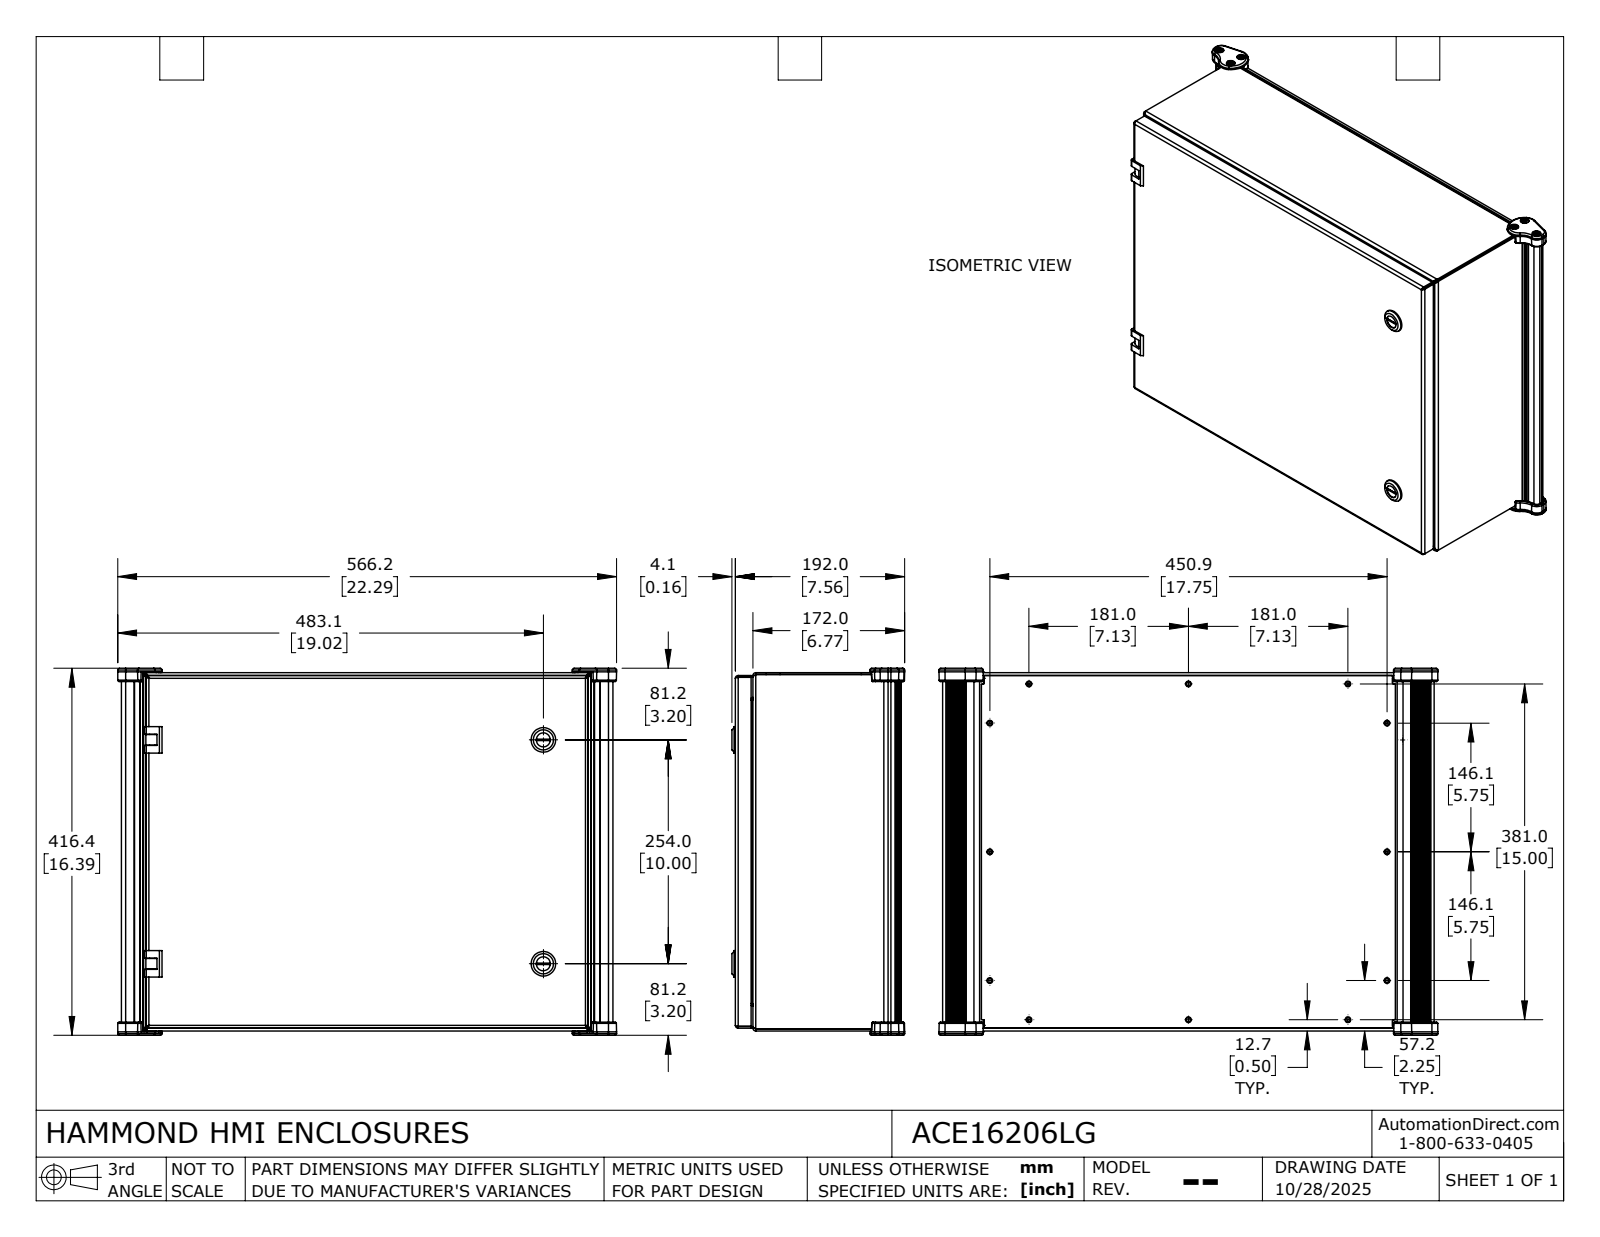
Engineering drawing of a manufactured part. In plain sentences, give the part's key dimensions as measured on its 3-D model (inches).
The part is named "ACE16206LG". Its 3-D file was written by "SolidWorks 2024 (AUTOMOTIVE_DESIGN)". It is 99 solids with 2540 faces: 1210 planar, 865 cylindrical and 465 other. Overall it measures 22.292 by 16.395 by 7.719 inches. Its volume is 151.8 cubic inches and its surface area 3 364 square inches. Round holes: 14 of diameter 0.156, 14 of diameter 0.234, 12 of diameter 0.19, 6 of diameter 0.205, 6 of diameter 0.413, 5 of diameter 0.196, 4 of diameter 0.159, 4 of diameter 0.406, 2 of diameter 0.16, 2 of diameter 0.197, 2 of diameter 0.232, 2 of diameter 0.25. Round bosses or shafts: 12 of diameter 0.256, 6 of diameter 0.25, 6 of diameter 0.19, 6 of diameter 0.149, 5 of diameter 0.236, 4 of diameter 0.375, 4 of diameter 0.33, 2 of diameter 1.1. Partial cylindrical surfaces (rounded edges, fillets, slot ends): 38 of radius 0.01, 30 of radius 0.059, 20 of radius 0.041, 20 of radius 0.122, 16 of radius 0.016, 16 of radius 0.03, 16 of radius 0.05, 14 of radius 0.039. The main face-to-face distances are 0.081, 0.125, 6.831, 6.912, 6.956, 7.037, 0.081, 0.206, 19.919, 6.706. The hole center spacings are 4, 10, 2.475, 5.049, 5.75, 7.125, 7.702, 8.915.
